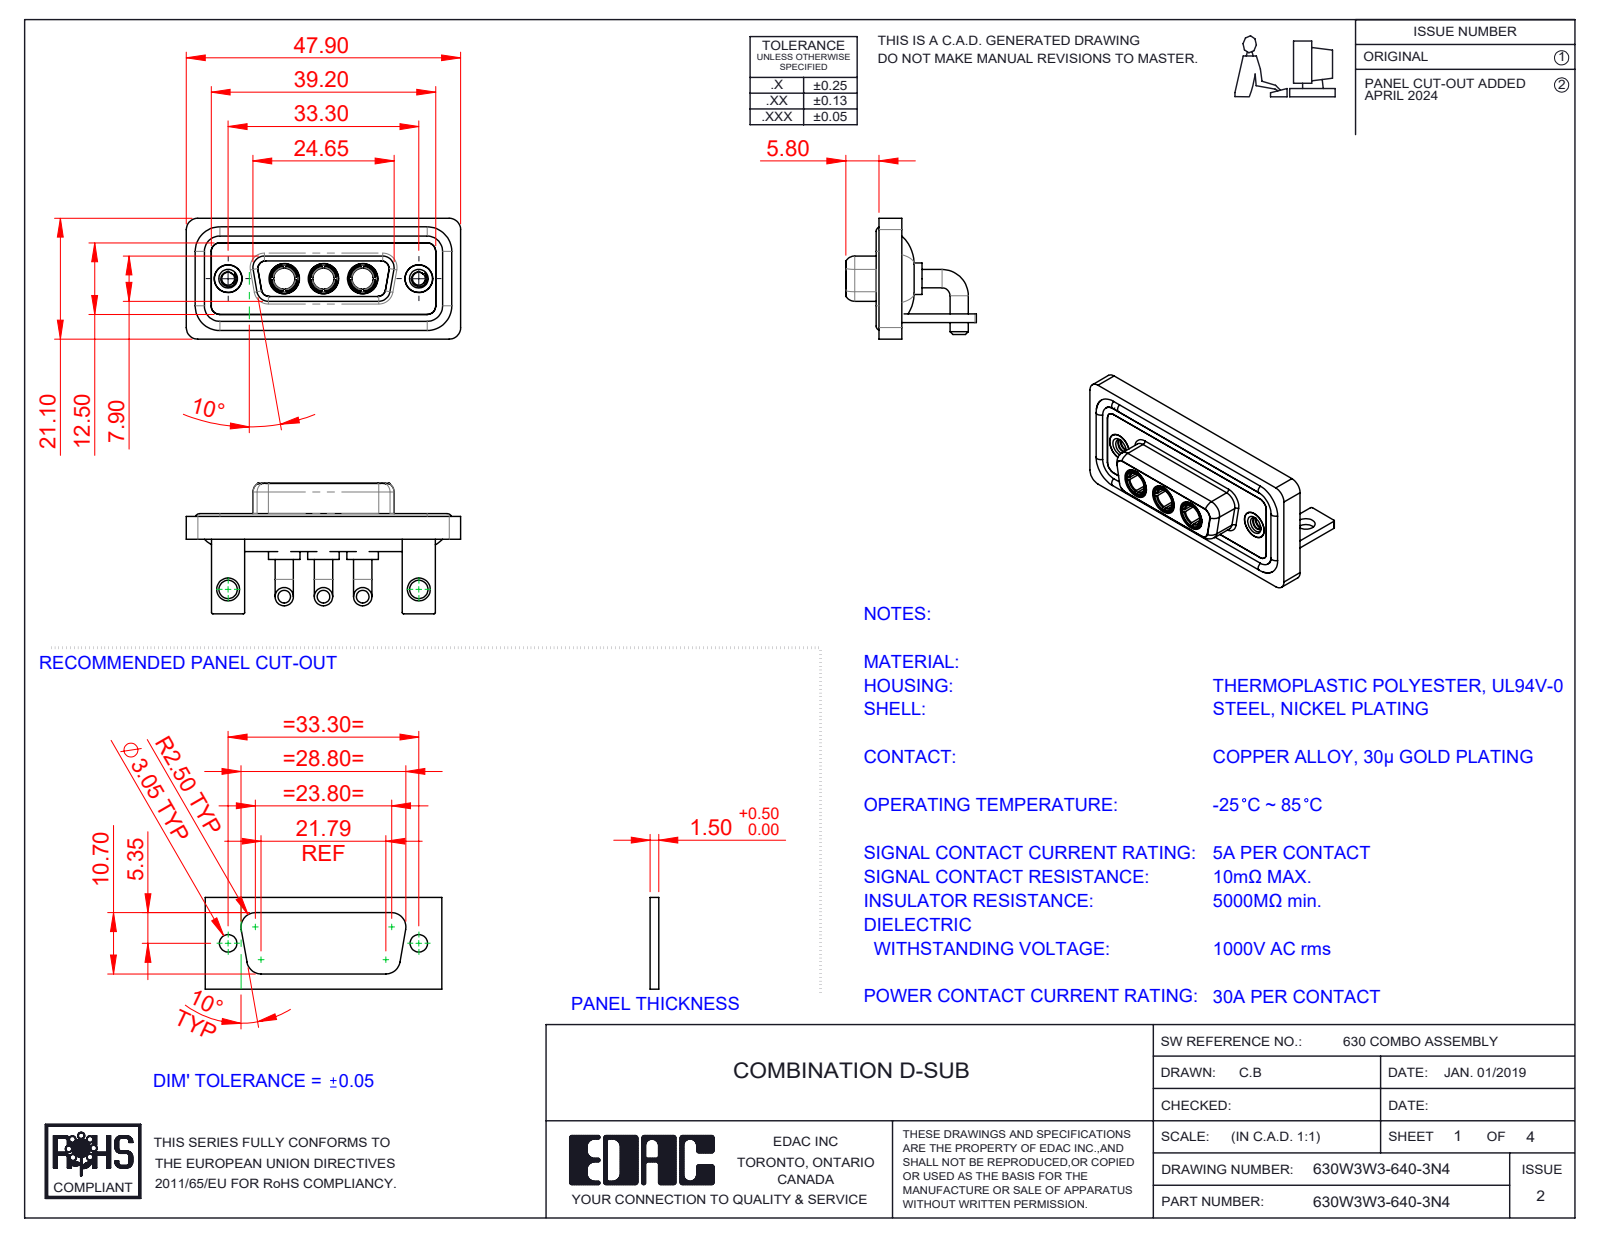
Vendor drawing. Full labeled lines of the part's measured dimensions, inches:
Part name (STEP PRODUCT): 630Combo Stabilizer Bracket_50 Contacts; Power Socket_30A RA; 630Combo Waterproof Housing_15 Contacts; 630W3W3-640-3N4 (+4 more)
STEP written by: SolidWorks 2023 (CONFIG_CONTROL_DESIGN)
Units: inches
Bodies: 15 solids, 668 faces (212 planar, 287 cylindrical, 169 other)
Overall size (bounding box): 1.886 × 0.898 × 0.831
Volume: 0.405 in³ · Surface area: 16.68 in²
Round holes (diameter × count): ⌀0.191 ×5, ⌀0.146 ×3, ⌀0.209 ×3, ⌀0.089 ×2, ⌀0.126 ×2, ⌀0.157 ×2, ⌀0.159 ×2, ⌀0.197 ×2
Round bosses / shafts (diameter × count): ⌀0.126 ×6, ⌀0.063 ×4, ⌀0.217 ×3, ⌀0.205 ×3, ⌀0.195 ×3, ⌀0.187 ×3, ⌀0.148 ×3, ⌀0.195 ×2
Partial cylindrical surfaces — rounded edges, fillets, slot ends (radius × count): R0.079 ×21, R0.059 ×18, R0.01 ×16, R0.053 ×12, R0.063 ×8, R0.02 ×5, R0.024 ×4, R0.026 ×4
Main face-to-face distances: 0.016, 0.114, 0.059, 0.071, 0.146, 0.043, 0.161, 0.063, 0.098, 0.055
Hole centre spacings: 0.27, 0.386, 0.656, 0.925, 1.311, 0.539
